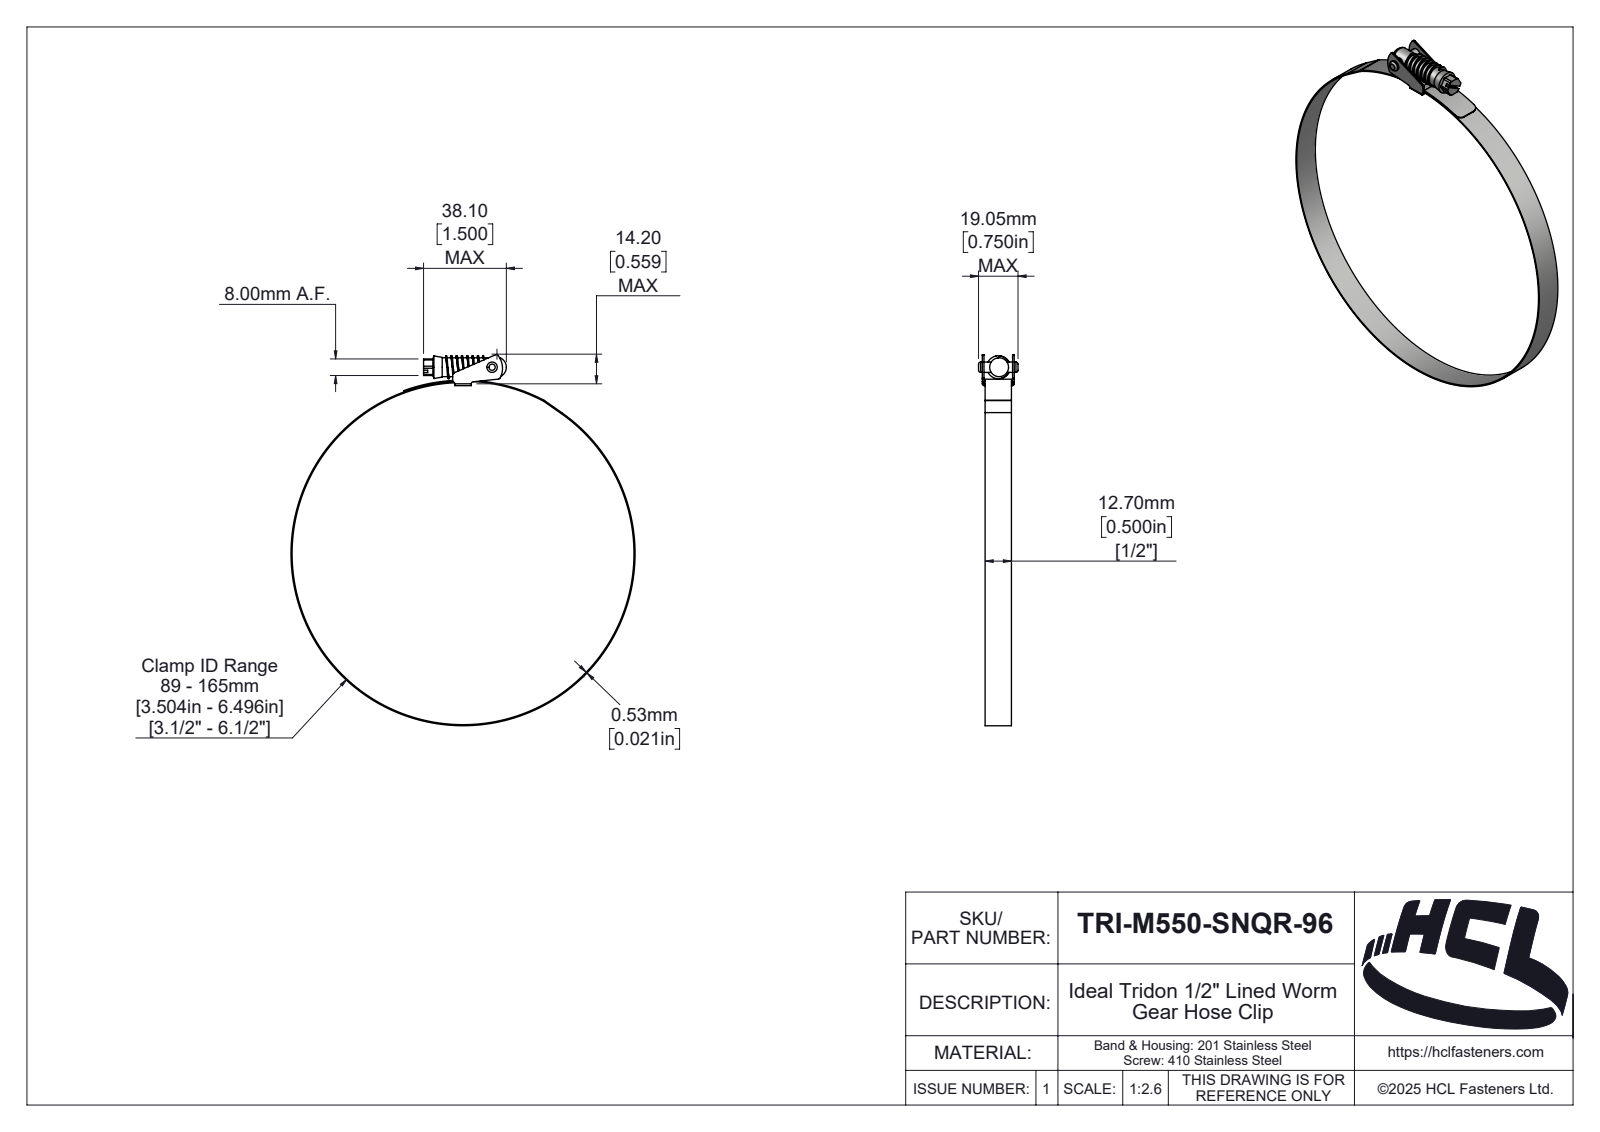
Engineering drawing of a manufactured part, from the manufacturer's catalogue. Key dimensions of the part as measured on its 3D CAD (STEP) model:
Part name (STEP PRODUCT): TRI-M550-SNQR-96
STEP written by: SolidWorks 2025 (AUTOMOTIVE_DESIGN)
Units: millimetres
Bodies: 5 solids, 222 faces (44 planar, 112 cylindrical, 66 other)
Overall size (bounding box): 179.02 × 166.06 × 19.05
Volume: 6 877 mm³ · Surface area: 18 122 mm²
Round holes (diameter × count): ⌀5 ×1, ⌀165 ×1
Round bosses / shafts (diameter × count): ⌀166.06 ×1, ⌀9.1 ×1
Partial cylindrical surfaces — rounded edges, fillets, slot ends (radius × count): R1 ×11, R0.1 ×2, R0.9 ×2, R3 ×2, R0.46 ×1, R1.89 ×1, R2 ×1, R2.35 ×1
Main face-to-face distances: 0.8, 1.35, 14.05, 14.6, 0.55, 13.25, 12.7, 15.4, 13.8, 0.53
Hole centre spacings: 90.99
